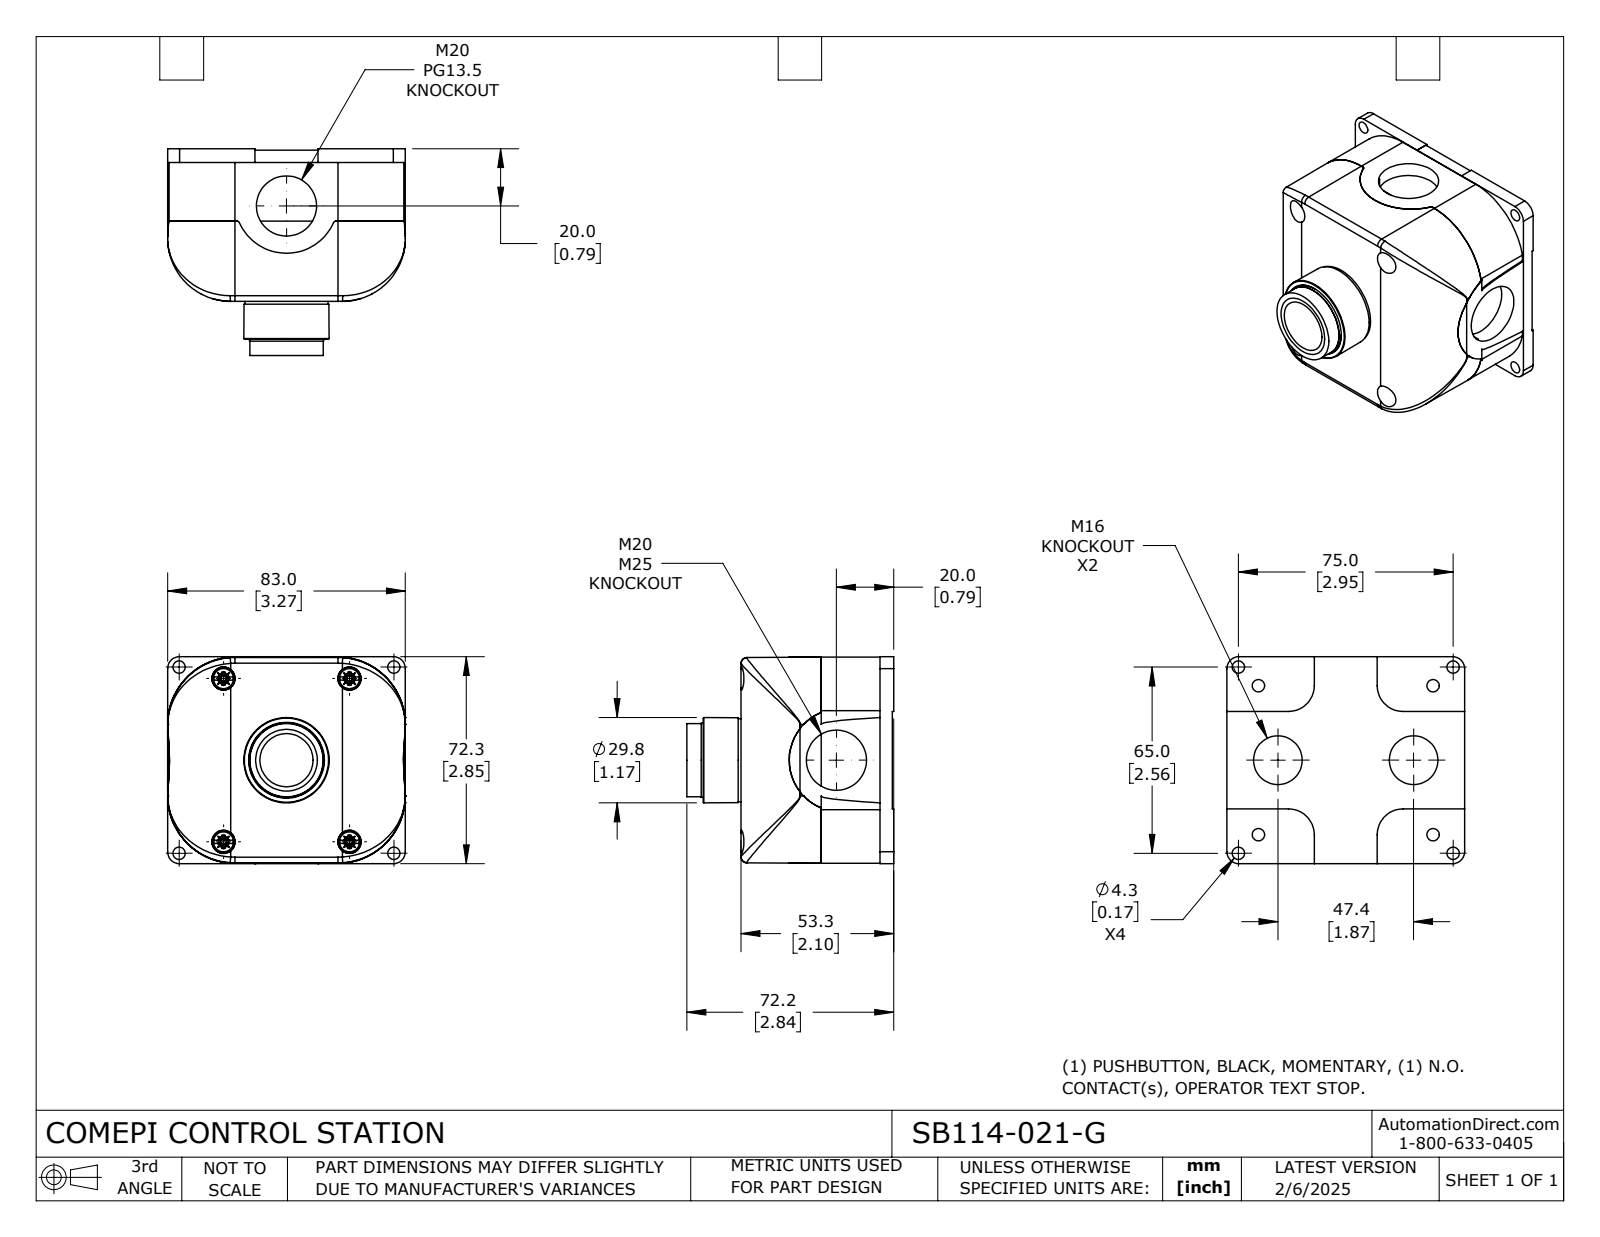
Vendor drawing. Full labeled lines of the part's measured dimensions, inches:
Part name (STEP PRODUCT): SB114-021-G
STEP written by: SolidWorks 2024 (CONFIG_CONTROL_DESIGN)
Units: inches
Bodies: 4 solids, 551 faces (301 planar, 146 cylindrical, 104 other)
Overall size (bounding box): 3.268 × 2.846 × 2.843
Volume: 12.98 in³ · Surface area: 90.08 in²
Round holes (diameter × count): ⌀0.169 ×8, ⌀0.323 ×4, ⌀0.669 ×2, ⌀0.827 ×2, ⌀0.531 ×1, ⌀0.713 ×1, ⌀0.854 ×1
Round bosses / shafts (diameter × count): ⌀0.276 ×4, ⌀1.142 ×1, ⌀1.02 ×1, ⌀1.008 ×1, ⌀0.748 ×1, ⌀0.728 ×1, ⌀0.63 ×1, ⌀0.614 ×1
Partial cylindrical surfaces — rounded edges, fillets, slot ends (radius × count): R0.035 ×4, R0.079 ×4, R0.354 ×4, R0.38 ×4, R0.925 ×4, R0.008 ×2, R0.01 ×2, R0.709 ×2
Main face-to-face distances: 0.976, 0.098, 0.878, 2.079, 1.98, 1.102, 0.118, 2.098, 0.02, 0.996
Hole centre spacings: 0.376, 1.058, 1.39, 1.578, 1.954, 2.32, 2.367, 2.689
